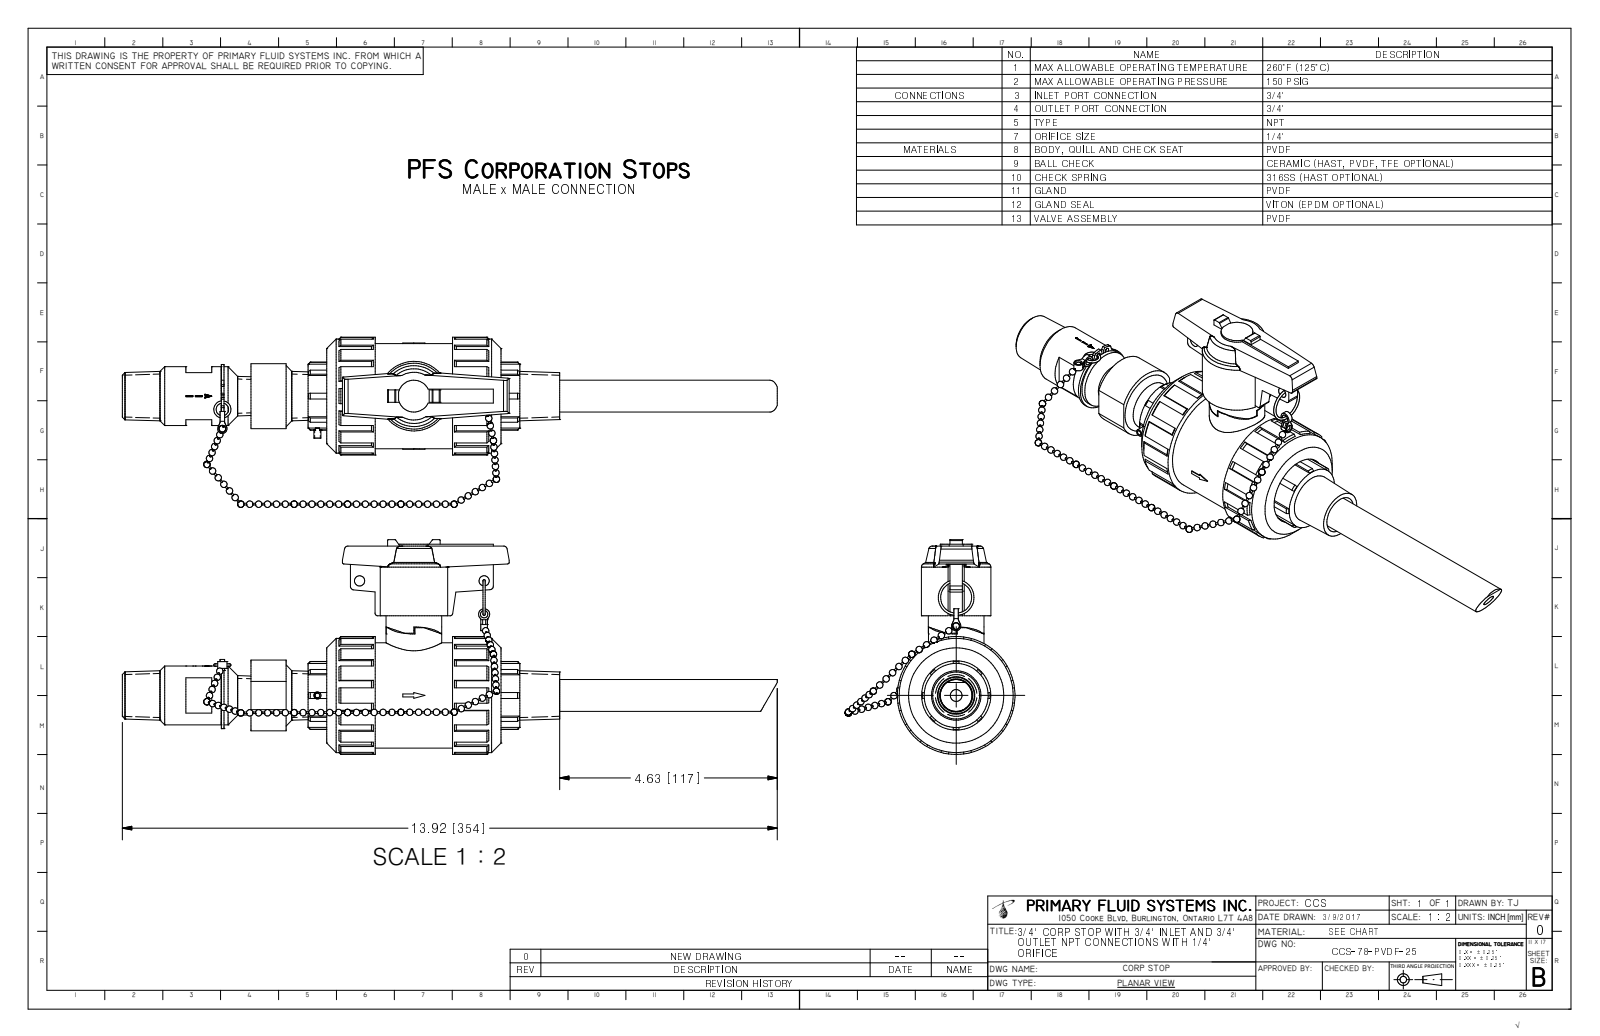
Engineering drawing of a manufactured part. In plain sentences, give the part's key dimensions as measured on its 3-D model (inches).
The part is named "CCS-78-PVDF-25_R0". Its 3-D file was written by "Autodesk Inventor 2009 (AUTOMOTIVE_DESIGN)". It is 1 solid with 611 faces: 293 planar, 77 cylindrical and 241 other. Overall it measures 13.922 by 4.554 by 3.61 inches. Its volume is 26.69 cubic inches and its surface area 126.3 square inches. Round holes: 1 of diameter 0.098, 1 of diameter 0.217, 1 of diameter 0.25, 1 of diameter 0.469, 1 of diameter 0.56, 1 of diameter 1.47, 1 of diameter 2.16. Round bosses or shafts: 1 of diameter 2.5, 1 of diameter 2.422, 1 of diameter 2.232, 1 of diameter 1.801, 1 of diameter 1.476, 1 of diameter 1.36, 1 of diameter 1.343, 1 of diameter 1.25. Partial cylindrical surfaces (rounded edges, fillets, slot ends): 4 of radius 0.02, 4 of radius 0.079, 2 of radius 0.039, 2 of radius 0.054, 2 of radius 0.059, 2 of radius 0.197, 1 of radius 0.337, 1 of radius 0.624. The main face-to-face distances are 0.039, 0.266, 0.306, 0.472, 3.233, 0.23, 3.475, 0.242, 3.003, 1.03. The hole center spacings are 0.657.
